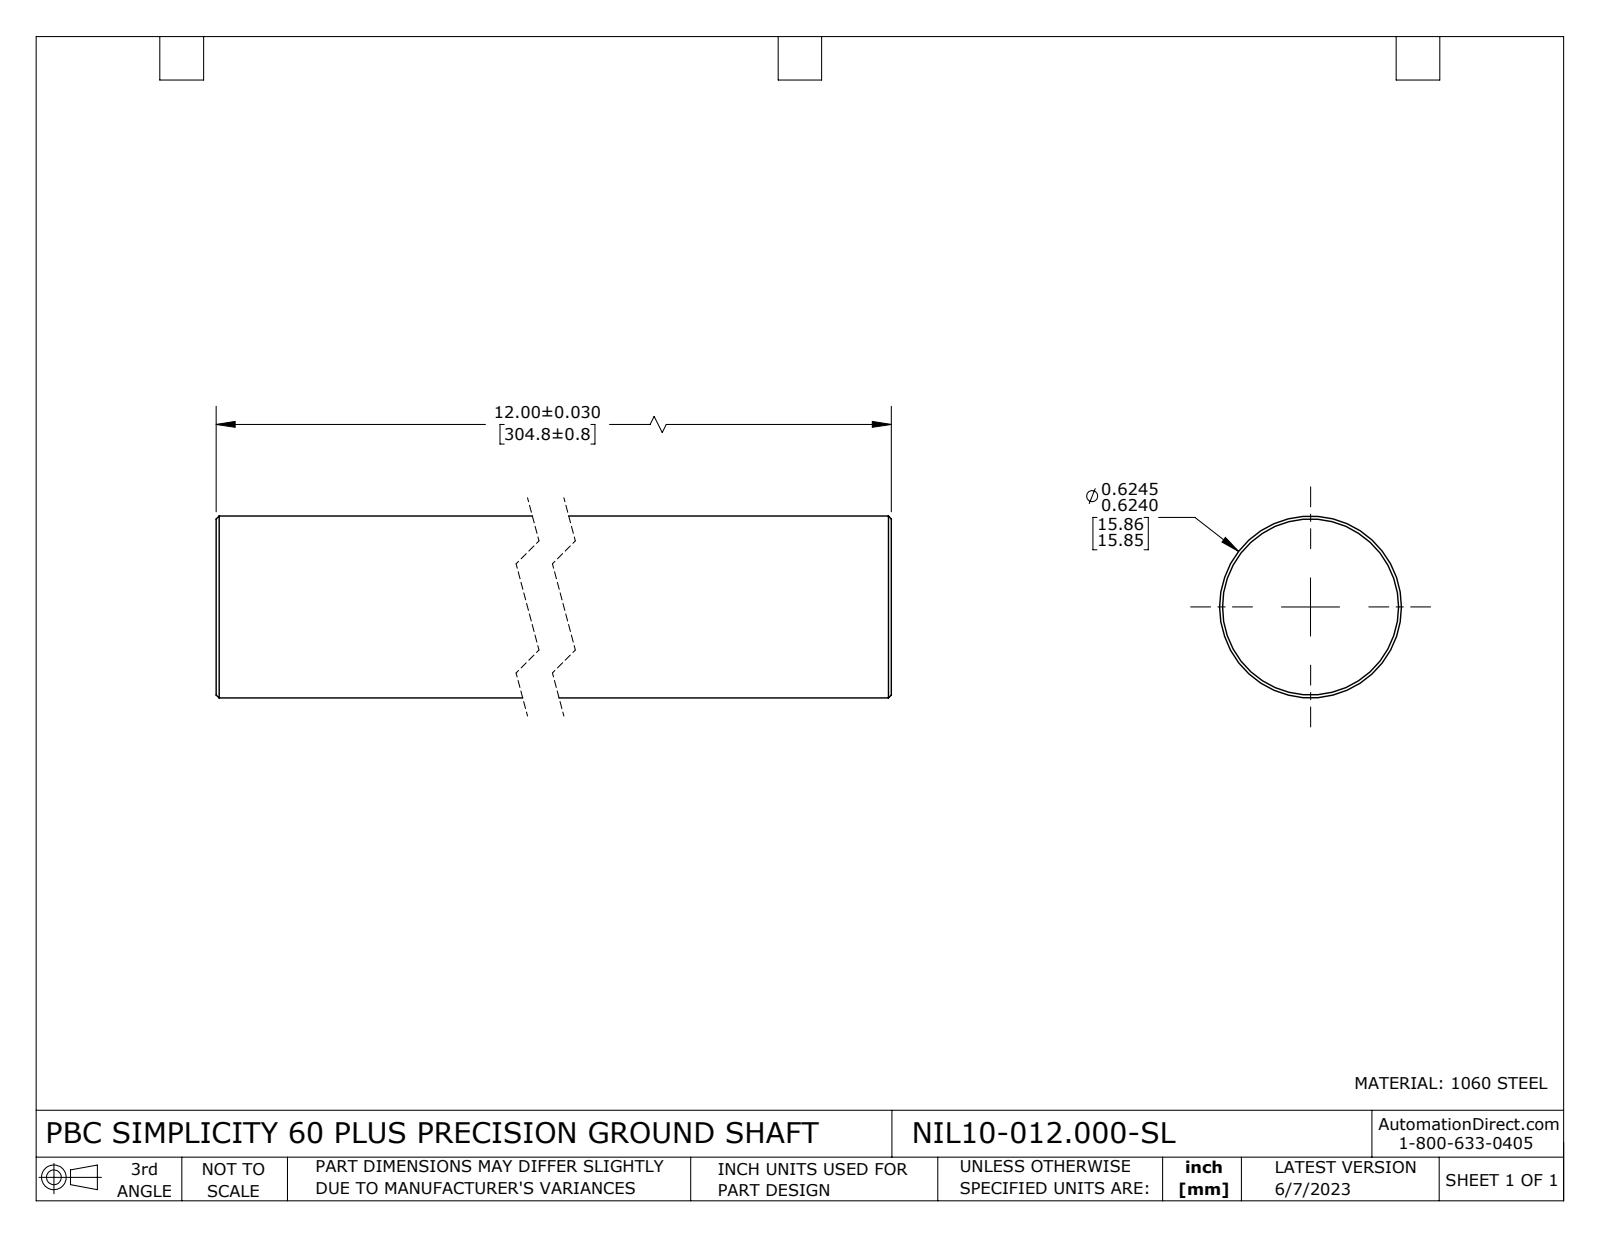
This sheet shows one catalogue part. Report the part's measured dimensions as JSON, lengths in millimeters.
{"part_name": "NIL10-012.000-SL", "step_written_by": "SolidWorks 2021 (CONFIG_CONTROL_DESIGN)", "units": "millimeters", "bodies": {"solids": 1, "faces": 8, "planar": 2, "cylindrical": 2, "other": 4}, "overall_size": [304.8, 15.9, 15.9], "volume_mm3": 60320, "surface_area_mm2": 15580, "round_bosses_or_shafts": [[15.9, 1]], "face_to_face_distances": [304.8]}
